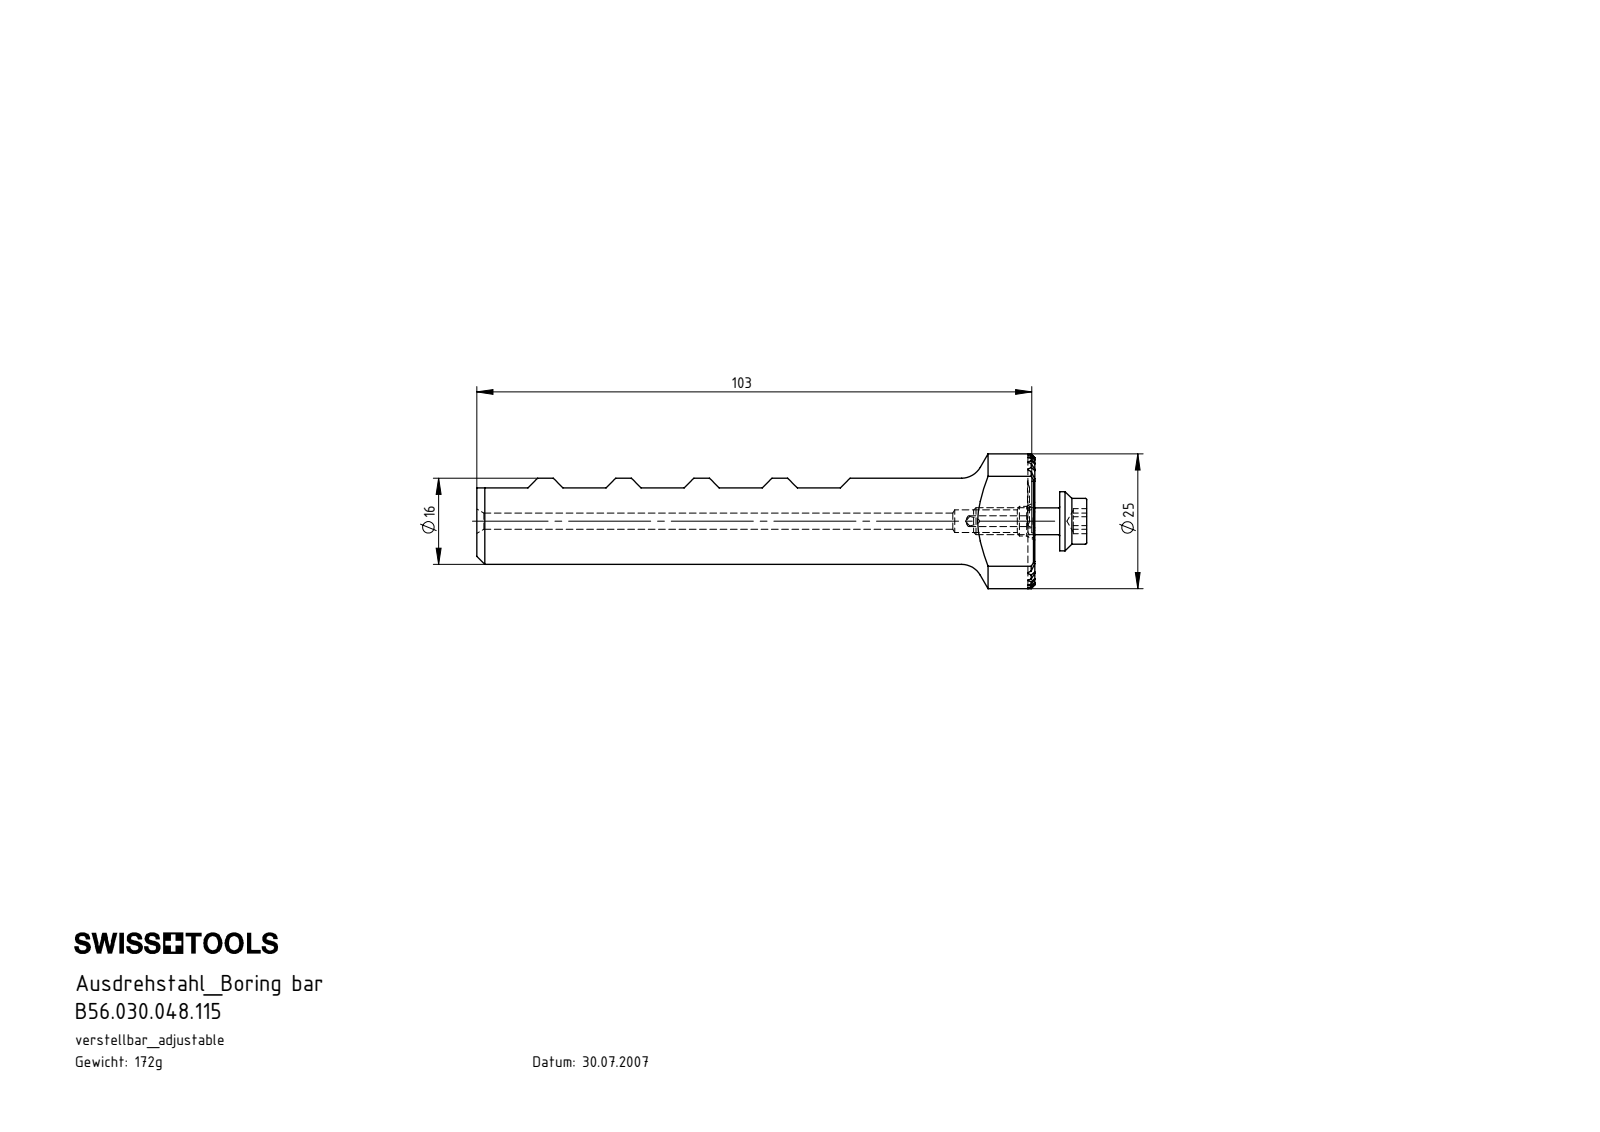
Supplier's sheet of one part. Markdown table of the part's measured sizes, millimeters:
| quantity | value |
| --- | --- |
| part name | B56.030.048.115; WCA-ER2.001.006_A; CCMT060204; BN 1392 - M5 x 16 (+2 more) |
| STEP written by | SolidWorks 2017 (CONFIG_CONTROL_DESIGN) |
| units | millimeters |
| bodies | 6 solids, 524 faces (245 planar, 111 cylindrical, 168 other) |
| overall size | 115 × 28.2 × 18.6 |
| volume | 24 821 mm³ |
| surface area | 10 711 mm² |
| round holes (diameter × count) | 2 × 4, 3 × 2, 2.05 × 1, 2.1 × 1, 2.8 × 1, 3.85 × 1, 4.2 × 1, 5.5 × 1 |
| round bosses / shafts (diameter × count) | 16 × 1, 11 × 1, 8.5 × 1, 5 × 1, 3.4 × 1, 2.5 × 1 |
| partial cylindrical surfaces (radius × count) | 0.14 × 19, 0.21 × 6, 0.36 × 5, 1.25 × 2, 2.7 × 2, 5.75 × 2, 0.36 × 1, 6 × 1 |
| main face-to-face distances | 1.73, 8.66, 6.93, 5.2, 3.46, 3.47, 18.6, 10.39, 1.74, 5.19 |
| hole center spacings | 3.73, 3.85, 7 |
